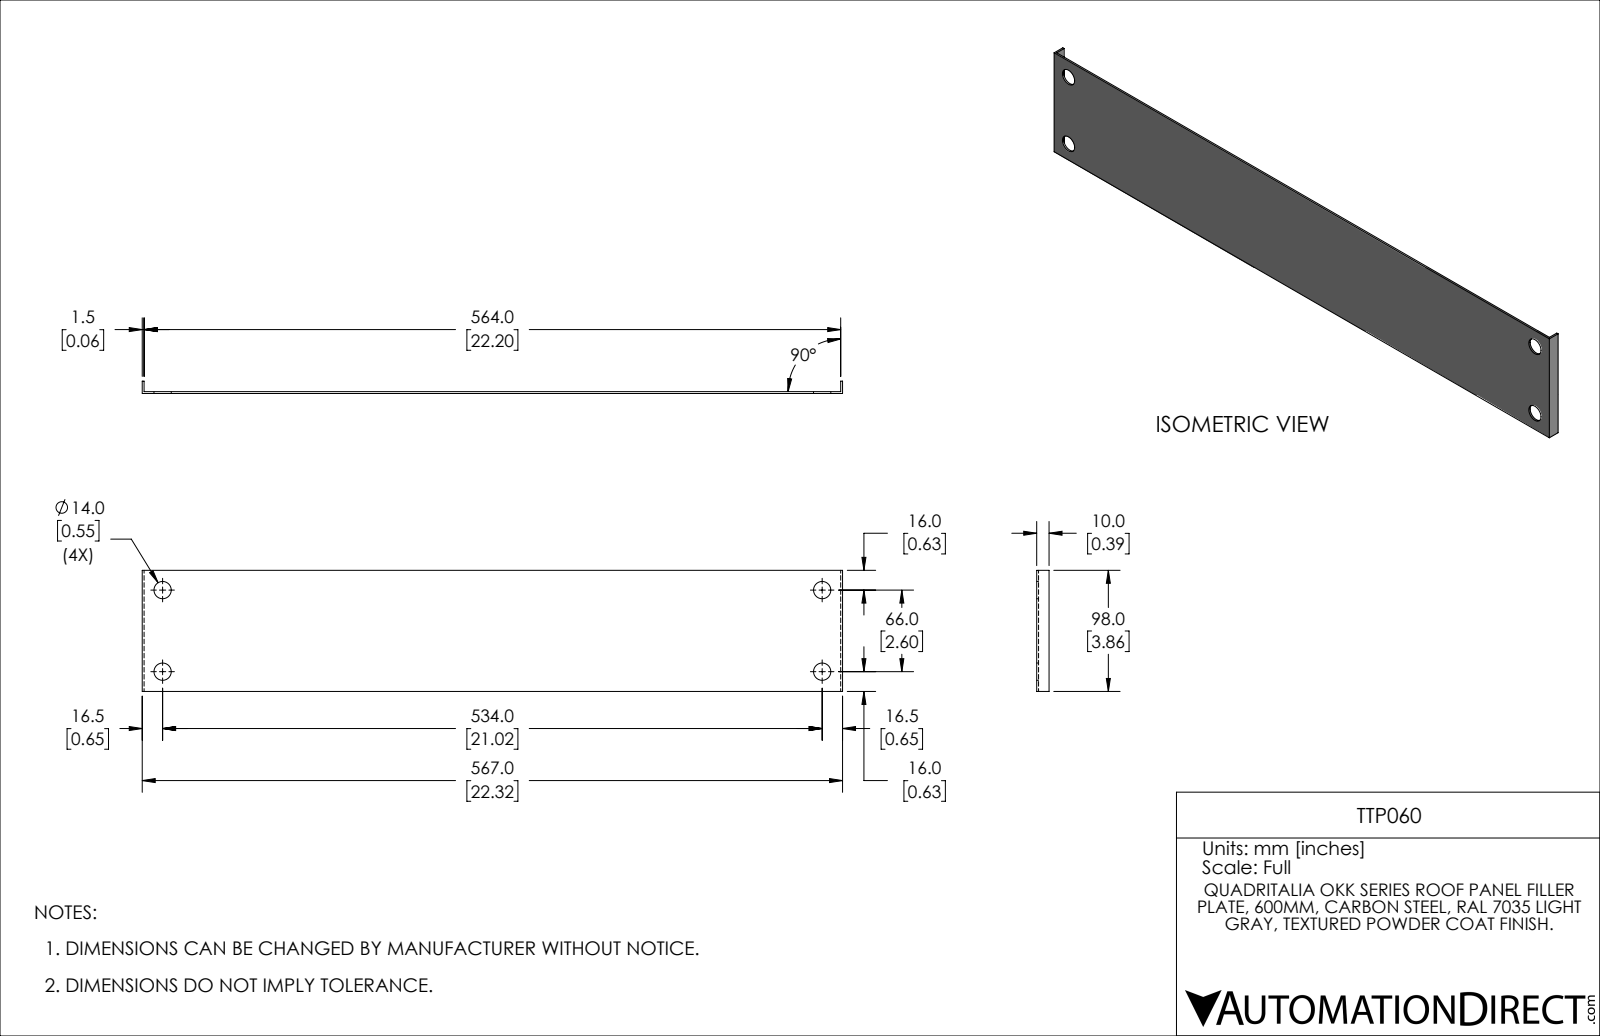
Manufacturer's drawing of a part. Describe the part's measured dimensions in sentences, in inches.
The part is named "TTP060". Its 3-D file was written by "SolidWorks 2021 (CONFIG_CONTROL_DESIGN)". It is 1 solid with 14 faces: 10 planar, 4 cylindrical and 0 other. Overall it measures 22.323 by 3.858 by 0.394 inches. Its volume is 5.182 cubic inches and its surface area 179.1 square inches. Round holes: 4 of diameter 0.551. The main face-to-face distances are 0.059, 22.264, 22.323, 3.858, 22.205, 0.335, 0.394. The hole center spacings are 2.598, 21.024, 21.183.
